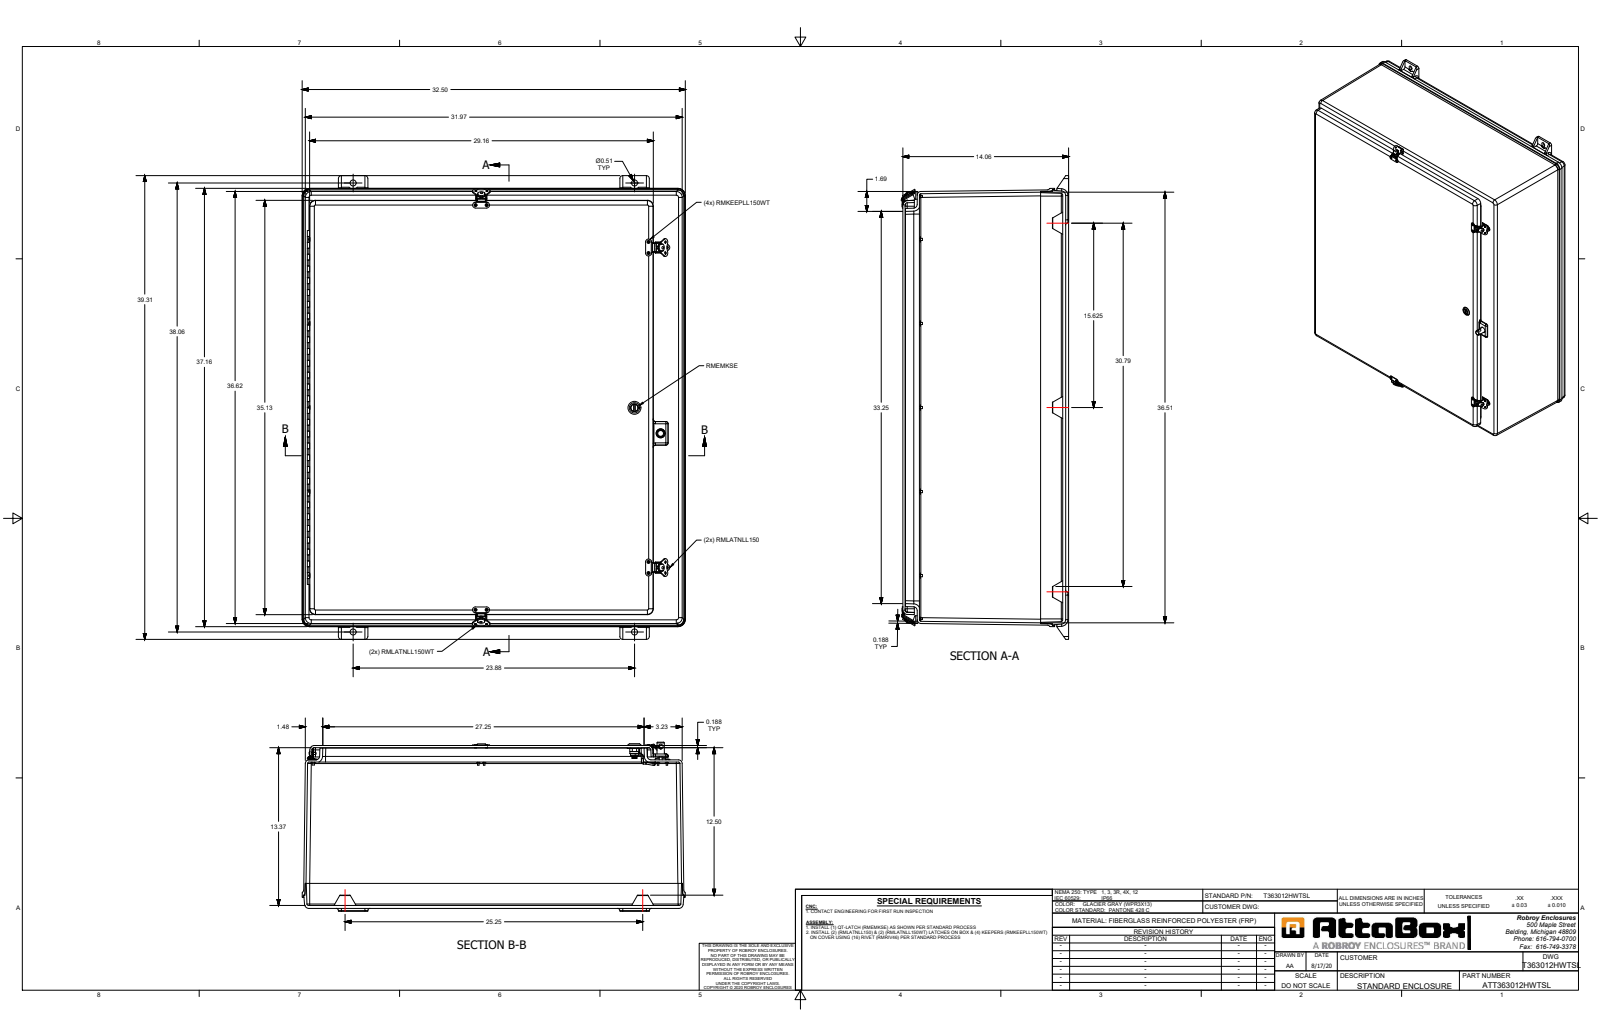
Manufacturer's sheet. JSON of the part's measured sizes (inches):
{"part_name": "T363012HWTSL", "step_written_by": "SolidWorks 2019 (AUTOMOTIVE_DESIGN)", "units": "inches", "bodies": {"solids": 94, "faces": 2121, "planar": 981, "cylindrical": 875, "other": 265}, "overall_size": [39.313, 32.5, 14.344], "volume_in3": 925.7, "surface_area_in2": 9308, "round_holes": [[0.201, 17], [0.1, 12], [0.133, 12], [0.14, 10], [0.104, 8], [0.13, 8], [0.187, 8], [0.075, 5], [0.191, 5], [0.208, 5], [0.135, 4], [0.139, 4]], "round_bosses_or_shafts": [[0.357, 10], [0.187, 10], [0.125, 10], [0.283, 8], [0.438, 5], [0.14, 5], [0.66, 4], [0.582, 4]], "partial_cylinders_radius": [[0.25, 34], [0.015, 32], [0.012, 30], [0.06, 17], [0.188, 17], [0.011, 16], [0.02, 16], [0.07, 16]], "face_to_face_distances": [0.188, 0.25, 13.81, 13.56, 13.622, 13.372, 1.216, 12.406, 12.156, 1.404], "hole_center_spacings": [14.25, 7.125, 7.125, 0.281, 21.375, 21.375, 28.5, 0.157]}
